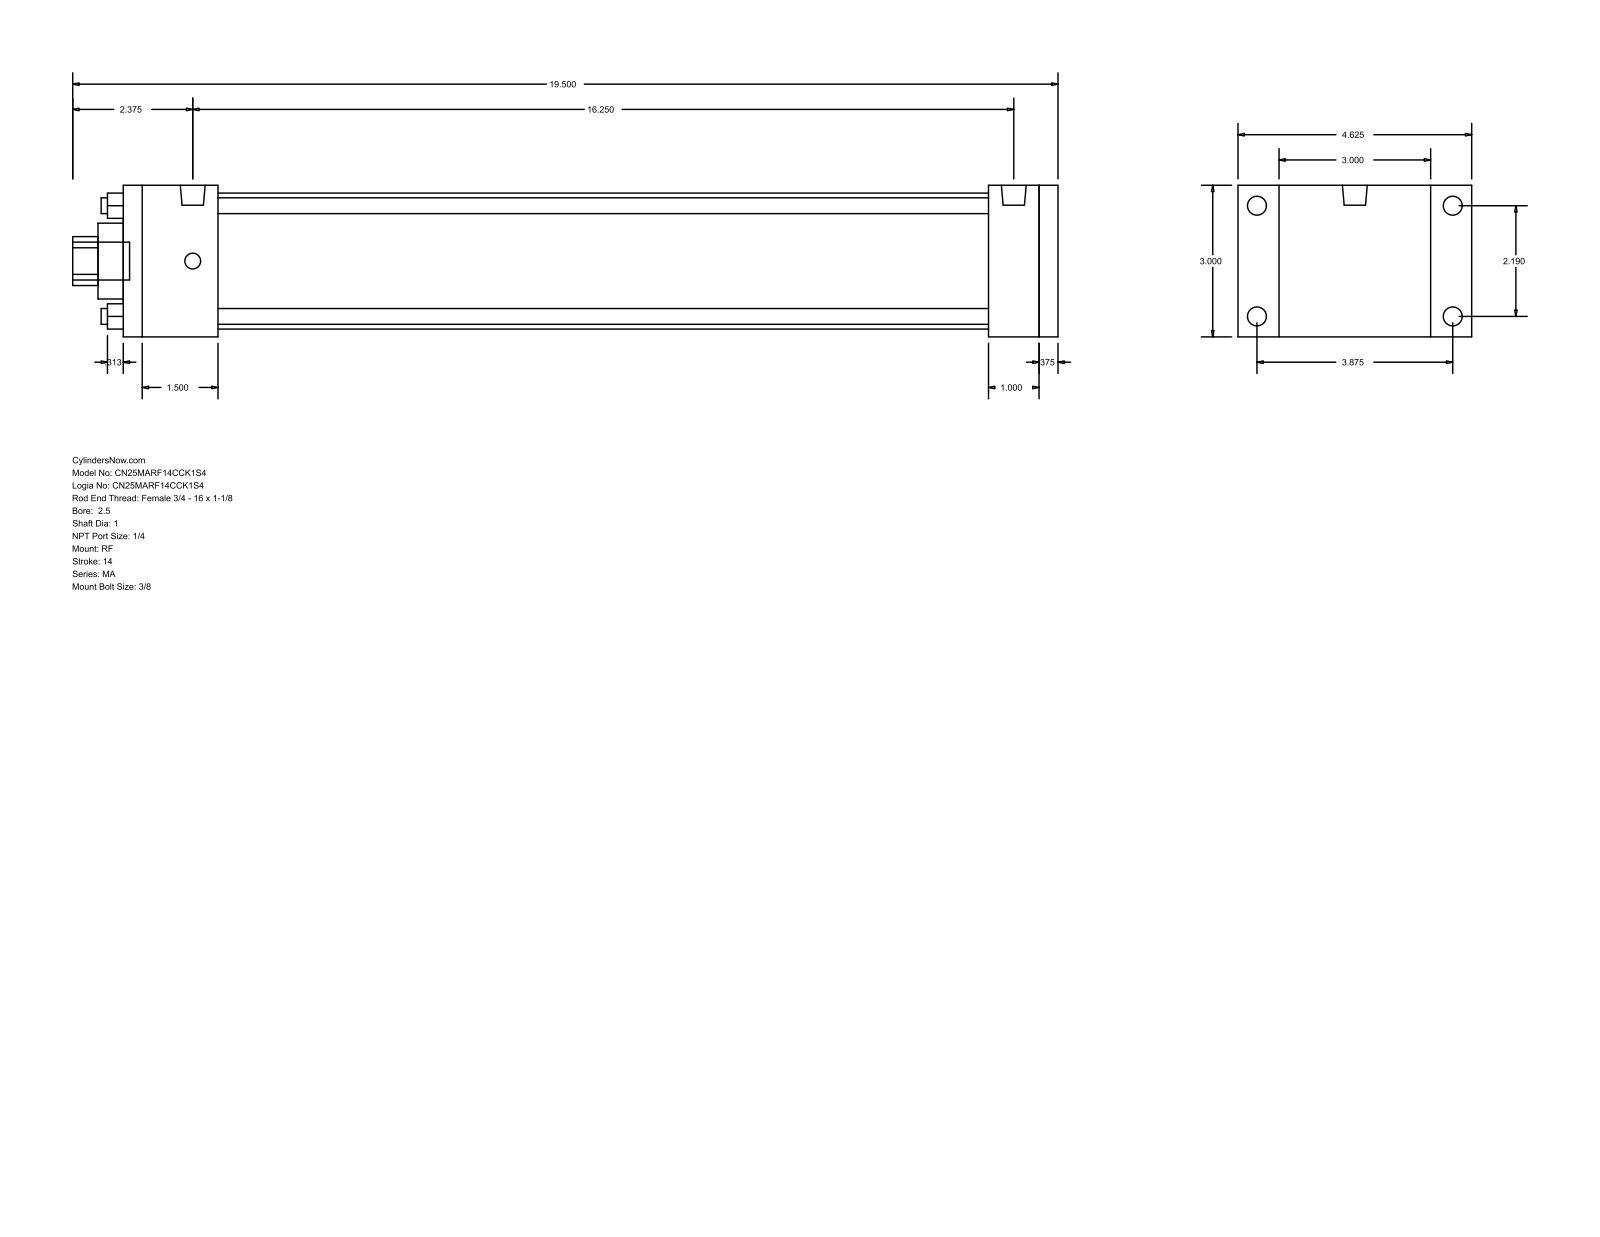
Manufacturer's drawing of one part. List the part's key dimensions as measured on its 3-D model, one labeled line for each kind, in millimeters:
Part name (STEP PRODUCT): MA_RF__0250_1
STEP written by: GSSL Pune (CONFIG_CONTROL_DESIGN)
Units: millimetres
Bodies: 0 solids, 92 faces (64 planar, 28 cylindrical, 0 other)
Overall size (bounding box): 495.3 × 117.47 × 76.2
Round holes (diameter × count): ⌀7.94 ×4, ⌀25.4 ×1, ⌀38.1 ×1, ⌀68.33 ×1
Round bosses / shafts (diameter × count): ⌀9.53 ×4, ⌀7.94 ×4, ⌀12.49 ×2, ⌀19.05 ×1
Partial cylindrical surfaces — rounded edges, fillets, slot ends (radius × count): R12.29 ×1
Main face-to-face distances: 76.2, 469.9, 9.53, 460.37, 47.63, 434.98, 387.35, 412.74, 422.27, 25.39
Hole centre spacings: 39.33, 55.62, 78.66
